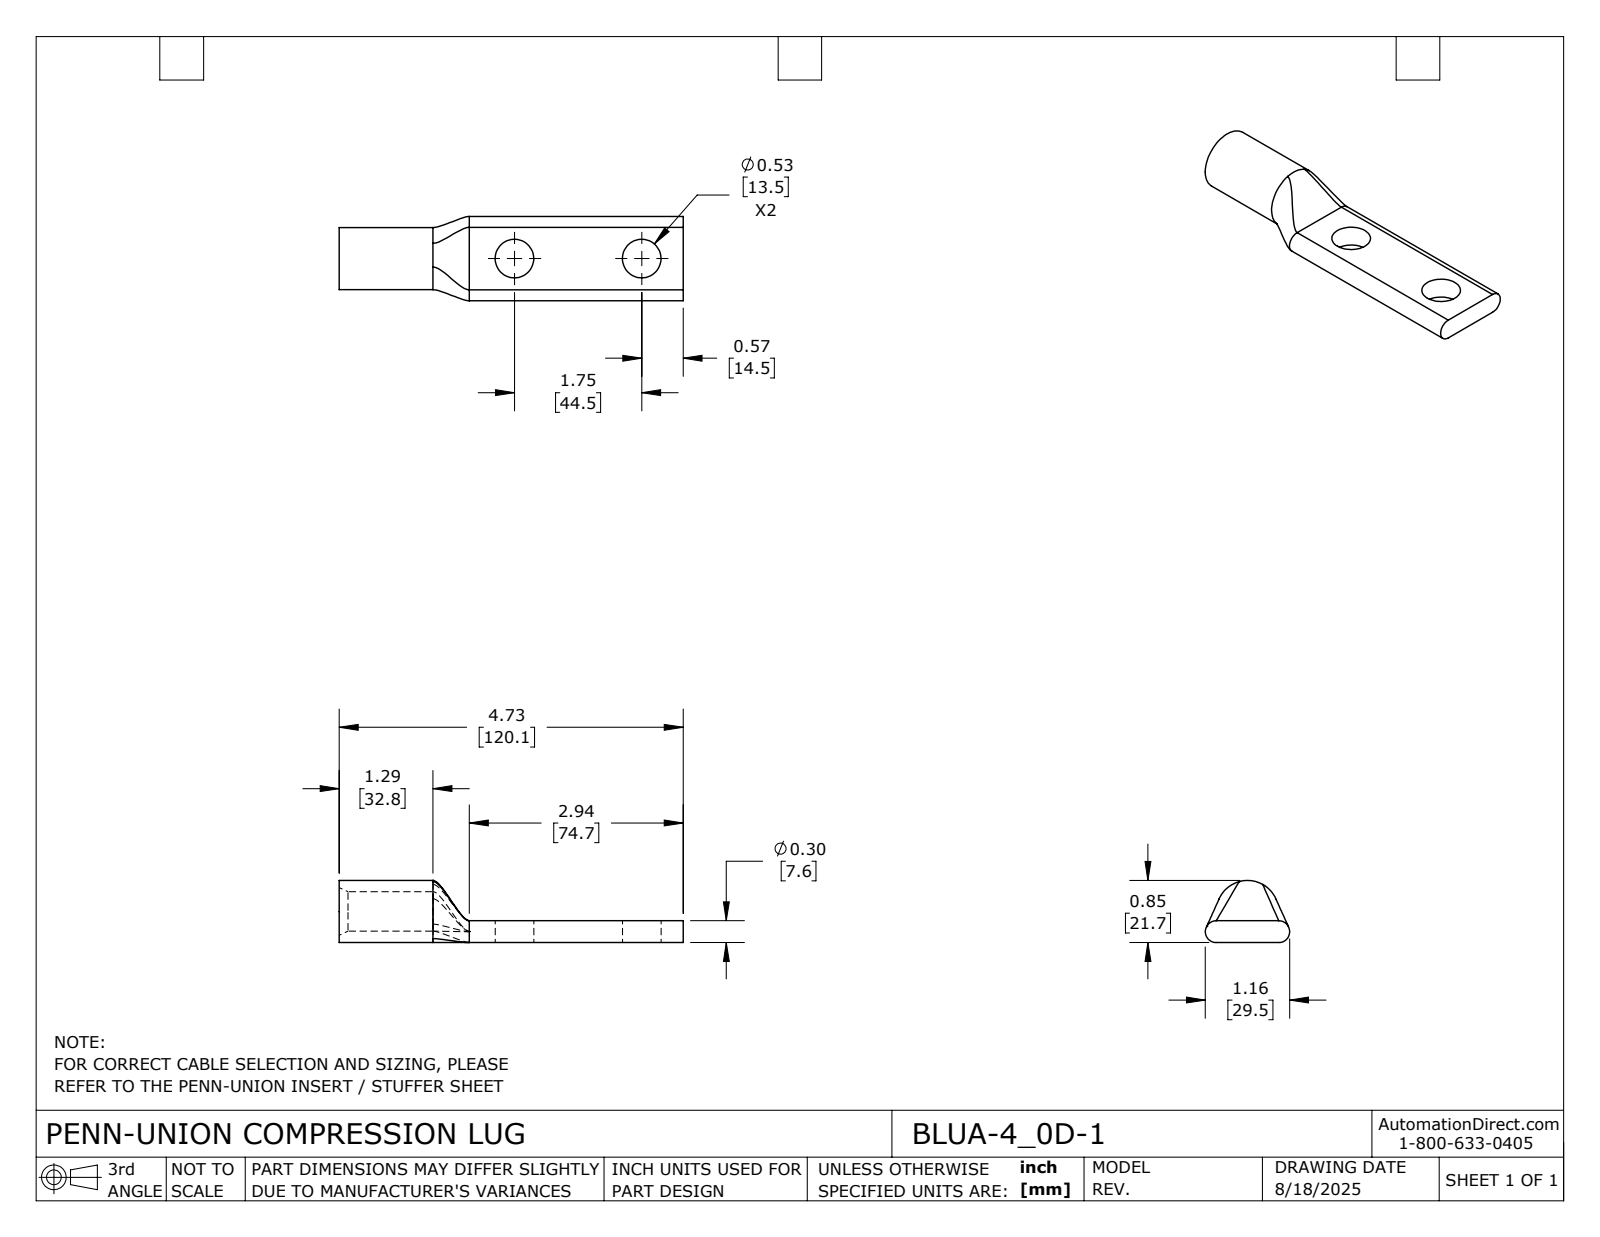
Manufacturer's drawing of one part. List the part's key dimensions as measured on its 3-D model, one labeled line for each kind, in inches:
Part name (STEP PRODUCT): BLUA-4_0D-1
STEP written by: SolidWorks 2024 (CONFIG_CONTROL_DESIGN)
Units: inches
Bodies: 1 solid, 26 faces (5 planar, 11 cylindrical, 10 other)
Overall size (bounding box): 4.73 × 1.16 × 0.854
Volume: 1.435 in³ · Surface area: 16.75 in²
Round holes (diameter × count): ⌀0.531 ×2, ⌀0.542 ×1
Round bosses / shafts (diameter × count): ⌀0.854 ×1
Partial cylindrical surfaces — rounded edges, fillets, slot ends (radius × count): R0.15 ×2
Main face-to-face distances: 0.3, 4.73, 1.79, 2.94
Hole centre spacings: 1.75
